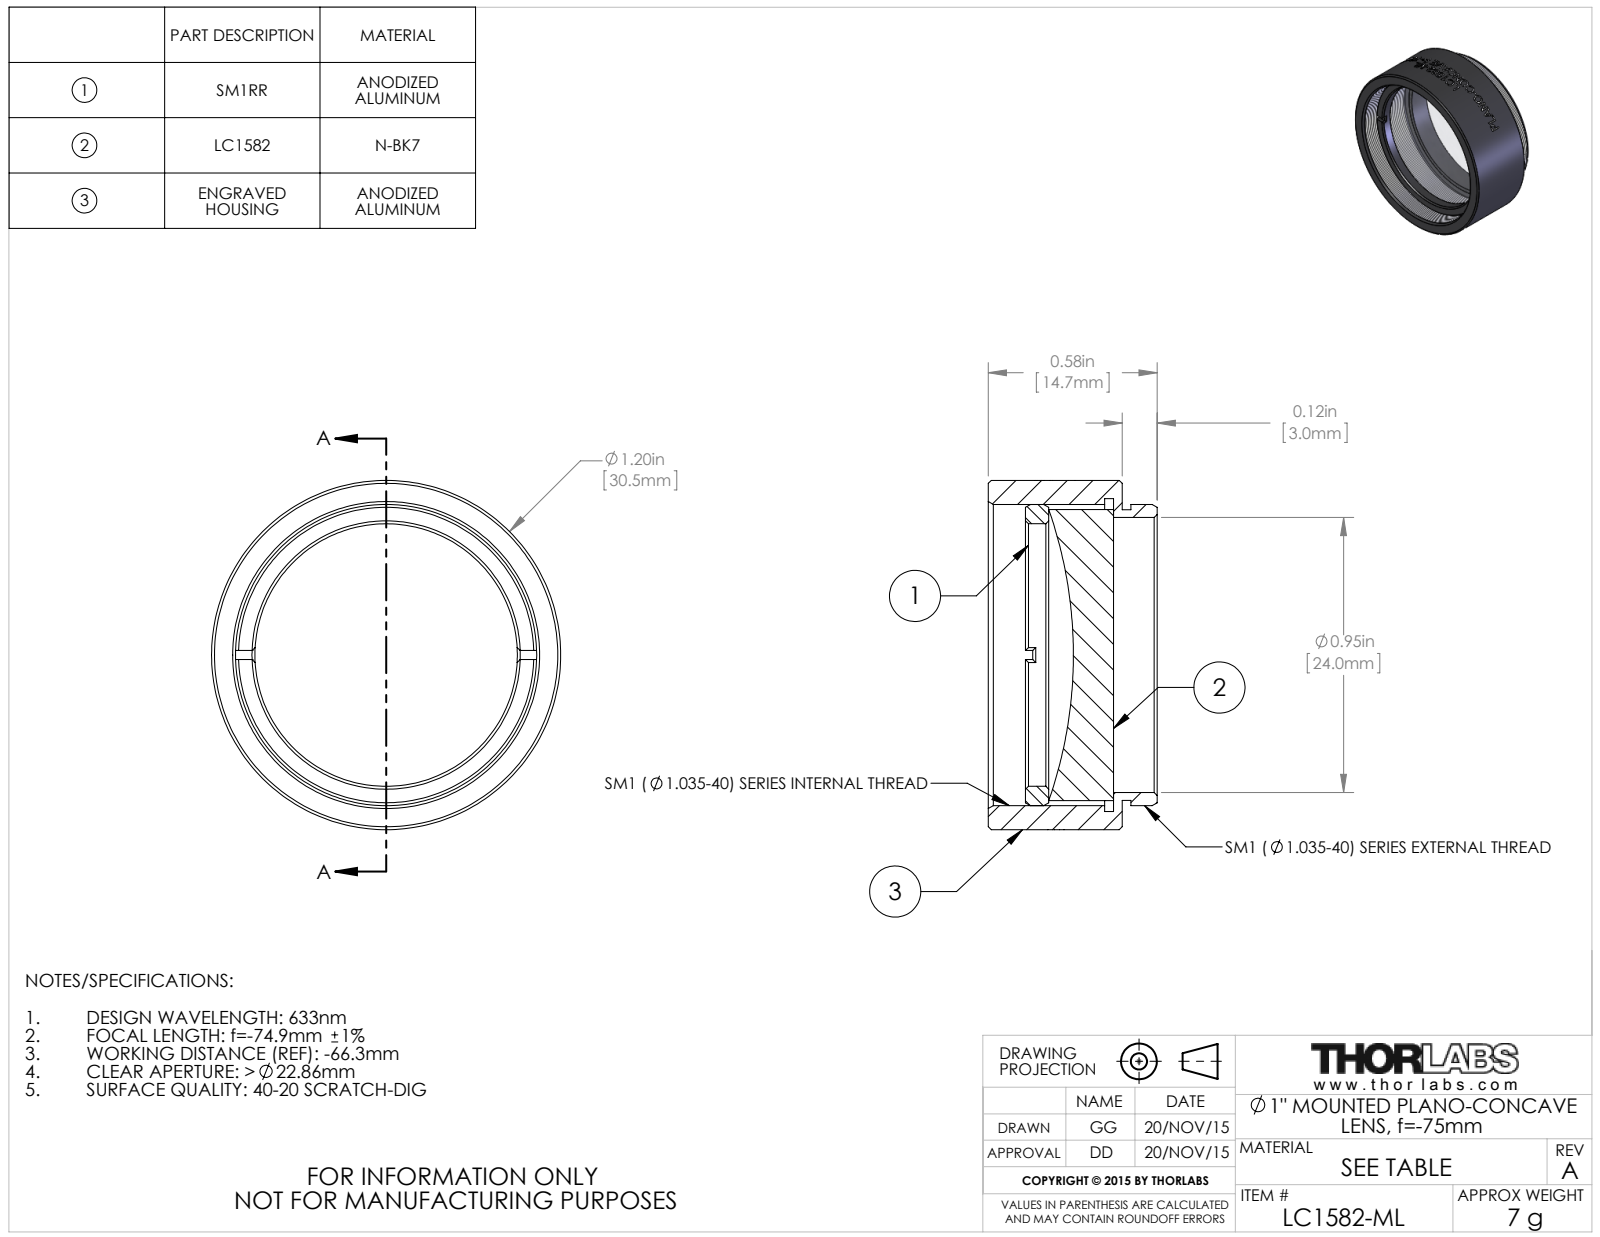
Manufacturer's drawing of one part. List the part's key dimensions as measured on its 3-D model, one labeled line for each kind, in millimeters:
Part name (STEP PRODUCT): TTN045289-E0W
STEP written by: SolidWorks 2014 (CONFIG_CONTROL_DESIGN)
Units: millimetres
Bodies: 3 solids, 116 faces (20 planar, 72 cylindrical, 24 other)
Overall size (bounding box): 30.5 × 30.5 × 14.7
Volume: 5 010 mm³ · Surface area: 5 207 mm²
Round holes (diameter × count): ⌀22.9 ×1, ⌀24 ×1, ⌀27.3 ×1
Round bosses / shafts (diameter × count): ⌀30.5 ×1, ⌀26.3 ×1, ⌀25.4 ×1, ⌀25.4 ×1
Main face-to-face distances: 0.8, 11.7, 10.9, 6.4, 5.6, 5.3, 8.5, 7.7, 2, 3.3
